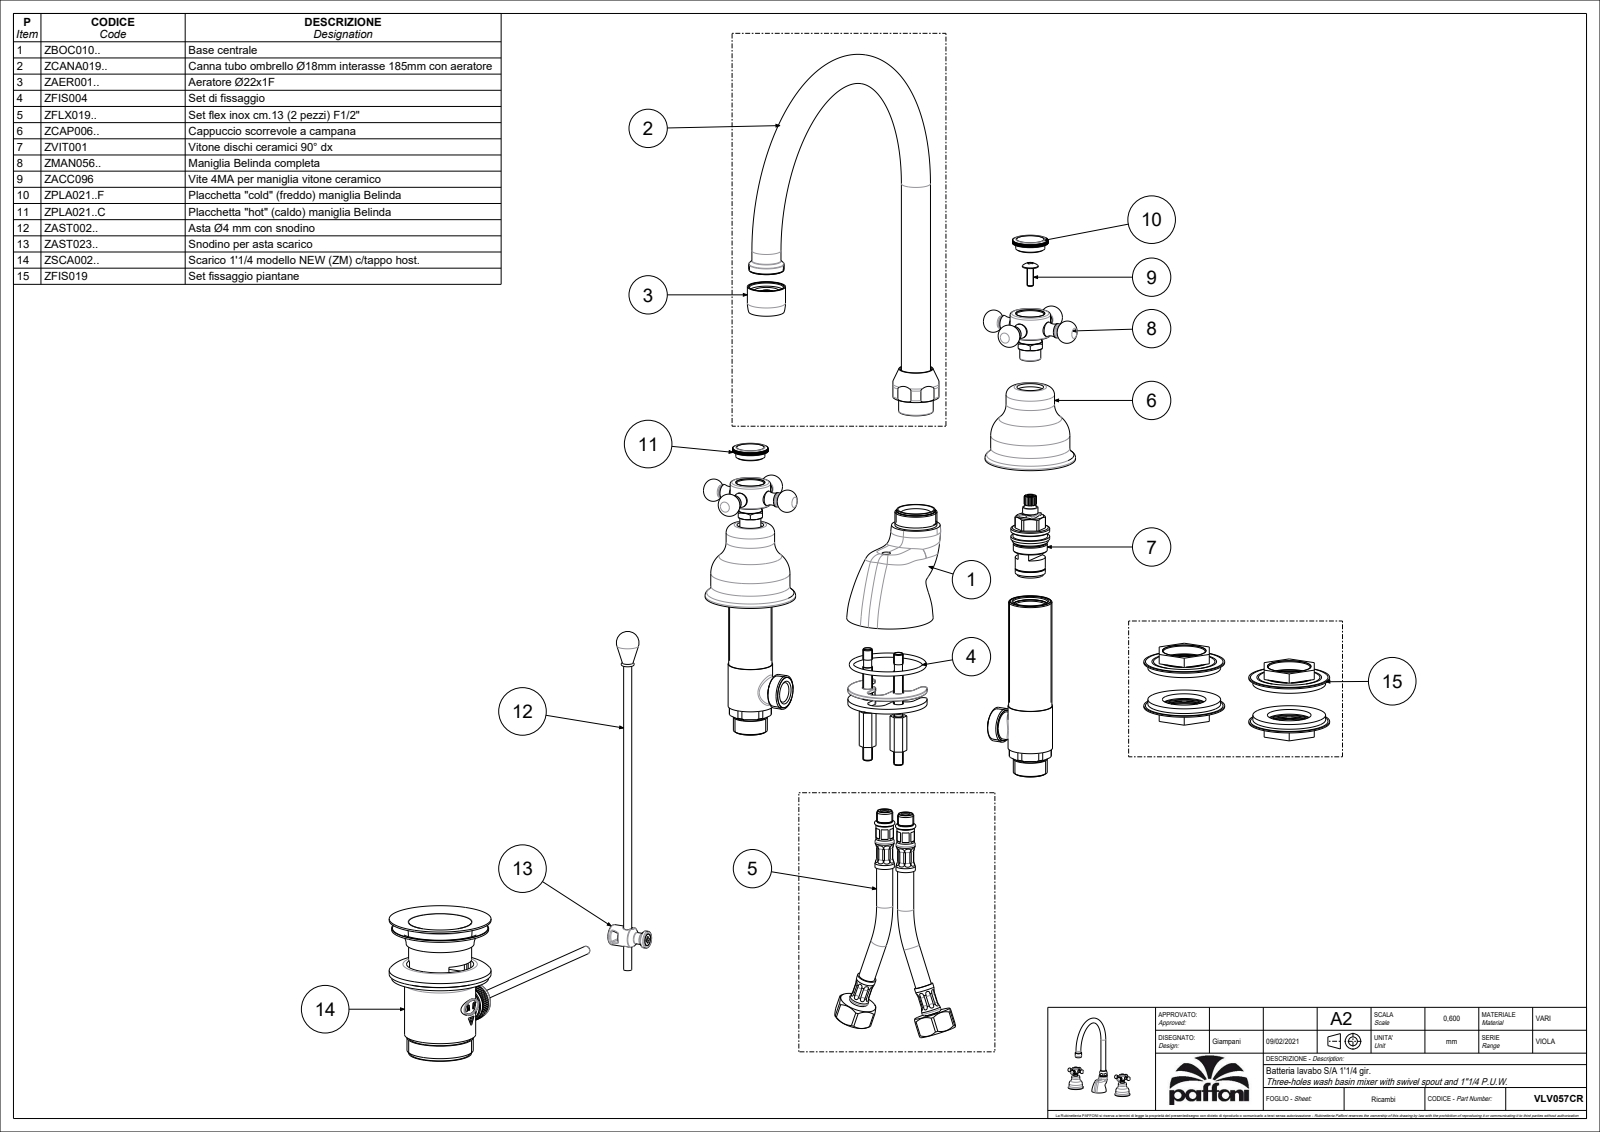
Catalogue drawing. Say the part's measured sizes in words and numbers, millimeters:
The part is named "VLV057CR". Its 3-D file was written by "CREO PARAMETRIC BY PTC INC, 2020044 (CONFIG_CONTROL_DESIGN)". It is 21 solids with 3396 faces: 2294 planar, 600 cylindrical and 502 other. Overall it measures 292 by 264.07 by 211.88 millimeters. Its volume is 161 259 cubic millimeters and its surface area 143 135 square millimeters. Round holes: 4 of diameter 5.2, 4 of diameter 11, 3 of diameter 17, 2 of diameter 3.3, 2 of diameter 4.5, 2 of diameter 8, 2 of diameter 8.8, 2 of diameter 9, 2 of diameter 10.3, 2 of diameter 10.5, 2 of diameter 16, 2 of diameter 16.2. Round bosses or shafts: 5 of diameter 6, 4 of diameter 18, 3 of diameter 9, 3 of diameter 7, 3 of diameter 5, 2 of diameter 55, 2 of diameter 49, 2 of diameter 29.5. Partial cylindrical surfaces (rounded edges, fillets, slot ends): 34 of radius 0.1, 4 of radius 0.5, 4 of radius 1, 4 of radius 1.5, 4 of radius 7.5, 2 of radius 2.5, 2 of radius 5, 2 of radius 9.4. The main face-to-face distances are 1, 5, 14, 57.2, 3, 6, 4, 10, 9, 67.2. The hole center spacings are 9.6, 13.31, 26.77, 92.69, 100, 100.12, 104.9, 107.67.
